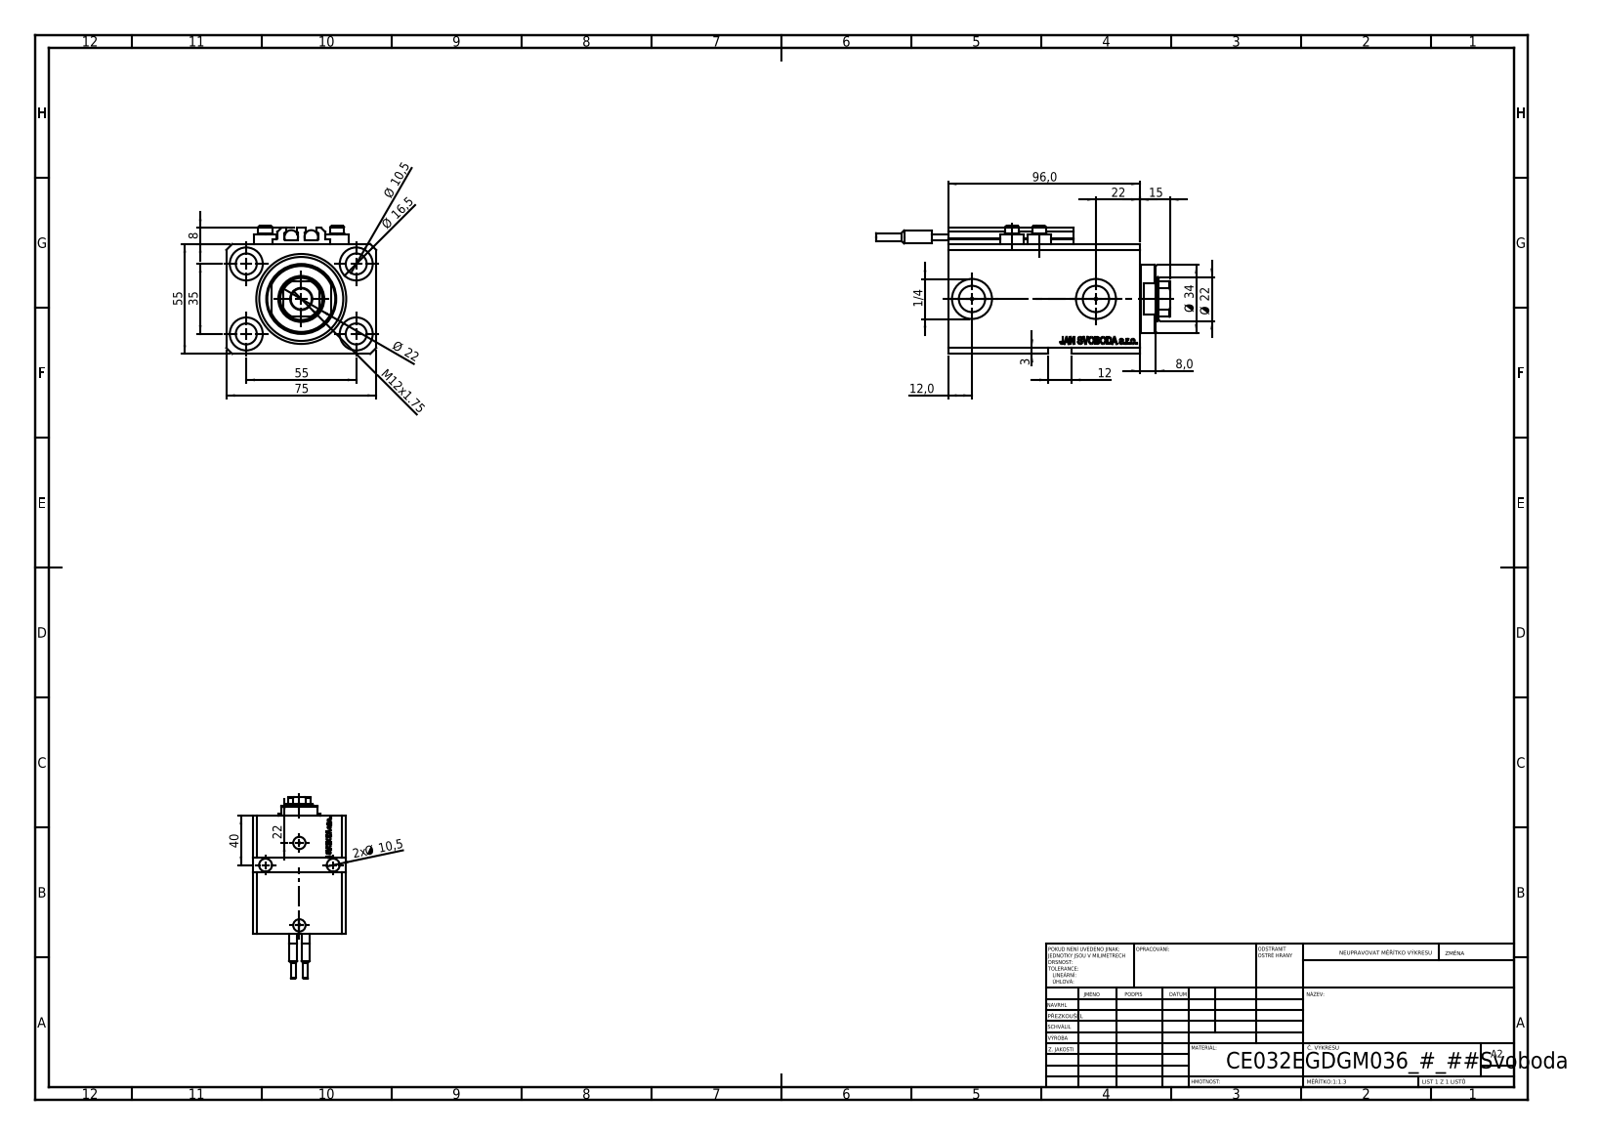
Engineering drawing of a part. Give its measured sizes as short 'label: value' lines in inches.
name: ALLEN BOLT V250CE; V250CE_VC_E; V250CE_C_VCP; SWITCH_V250CE (+1 more)
written by: SolidWorks 2019 (CONFIG_CONTROL_DESIGN)
unit: in
bodies: 10 solids, 1132 faces (550 planar, 150 cylindrical, 432 other)
size: 5.787 × 2.953 × 2.52
volume: 20.7 in³; area: 137.7 in²
holes: 7× ⌀0.413, 4× ⌀0.049, 4× ⌀0.157, 4× ⌀0.65, 2× ⌀0.394, 2× ⌀0.518, 2× ⌀0.787, 1× ⌀0.866, 1× ⌀1.26, 1× ⌀1.772
bosses: 4× ⌀0.457, 4× ⌀0.276, 2× ⌀0.268, 2× ⌀0.256, 2× ⌀0.157, 1× ⌀1.339
rounds: 10× R0.008, 1× R0.413
face distances: 2.165, 2.953, 0.118, 0.591, 3.78, 3.189, 0.39, 2.244, 2.799, 3.39
hole spacings: 1.283, 2.165, 0.535, 0.555, 1.016, 1.196, 1.213, 1.294
